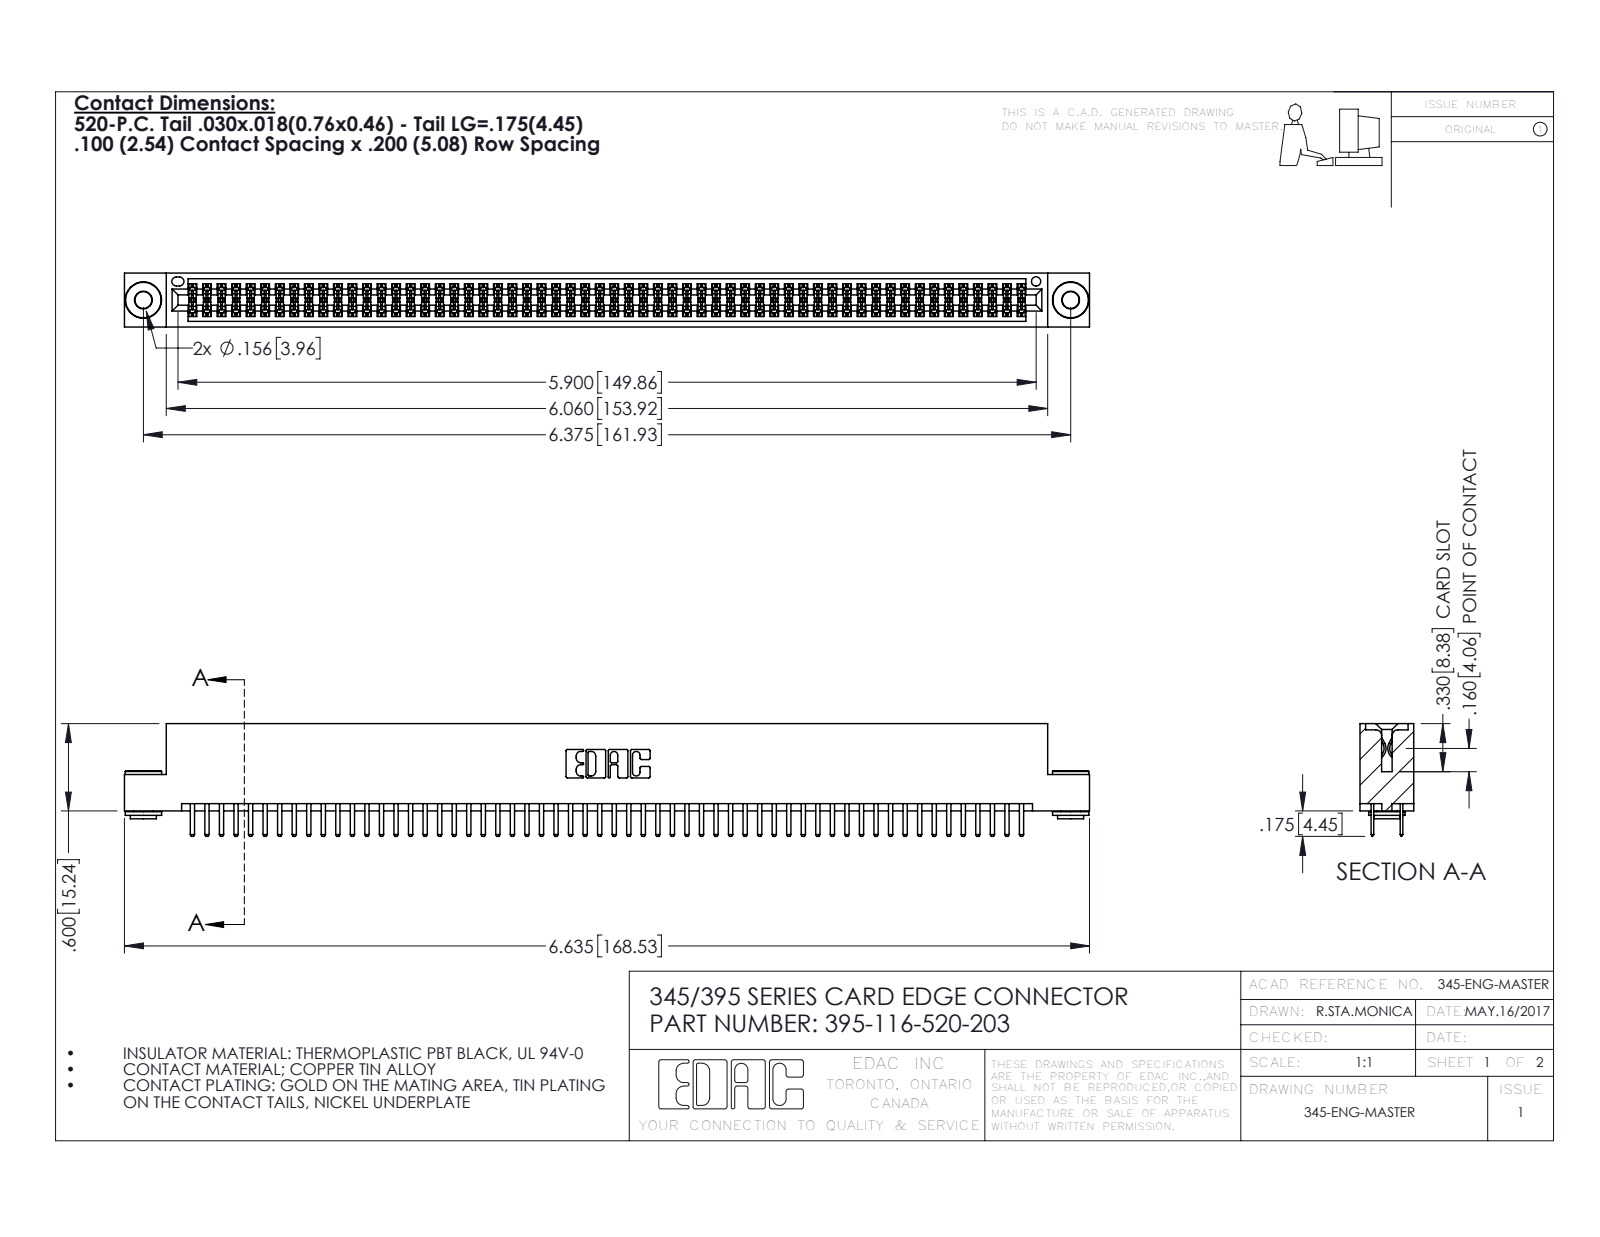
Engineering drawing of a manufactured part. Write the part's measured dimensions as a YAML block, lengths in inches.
part_name: "395-116-520-203; 345-250-002_345-250-002-102; 345 Part_Flush Mounting Lugs - 0.156 Dia-TH; 345-292-001_345-293-120"
step_written_by: "SolidWorks 2016 (CONFIG_CONTROL_DESIGN)"
units: inches
bodies: {solids: 119, faces: 6428, planar: 4150, cylindrical: 2270, other: 8}
overall_size: [6.635, 0.775, 0.37]
volume: 1.006
surface_area: 38.41
round_holes:
  - {diameter: 0.116, count: 2}
  - {diameter: 0.156, count: 2}
  - {diameter: 0.064, count: 1}
round_bosses_or_shafts:
  - {diameter: 0.25, count: 2}
  - {diameter: 0.18, count: 2}
  - {diameter: 0.136, count: 2}
partial_cylinders:
  - {radius: 0.006, count: 174}
  - {radius: 0.01, count: 120}
  - {radius: 0.01, count: 22}
  - {radius: 0.007, count: 6}
  - {radius: 0.031, count: 6}
  - {radius: 0.026, count: 3}
  - {radius: 0.014, count: 2}
  - {radius: 0.019, count: 2}
face_to_face_distances: [0.072, 0.298, 0.2, 0.37, 0.025, 0.098, 0.272, 0.225, 0.022, 0.072]
hole_center_spacings: [0.27, 6.139, 6.375]
